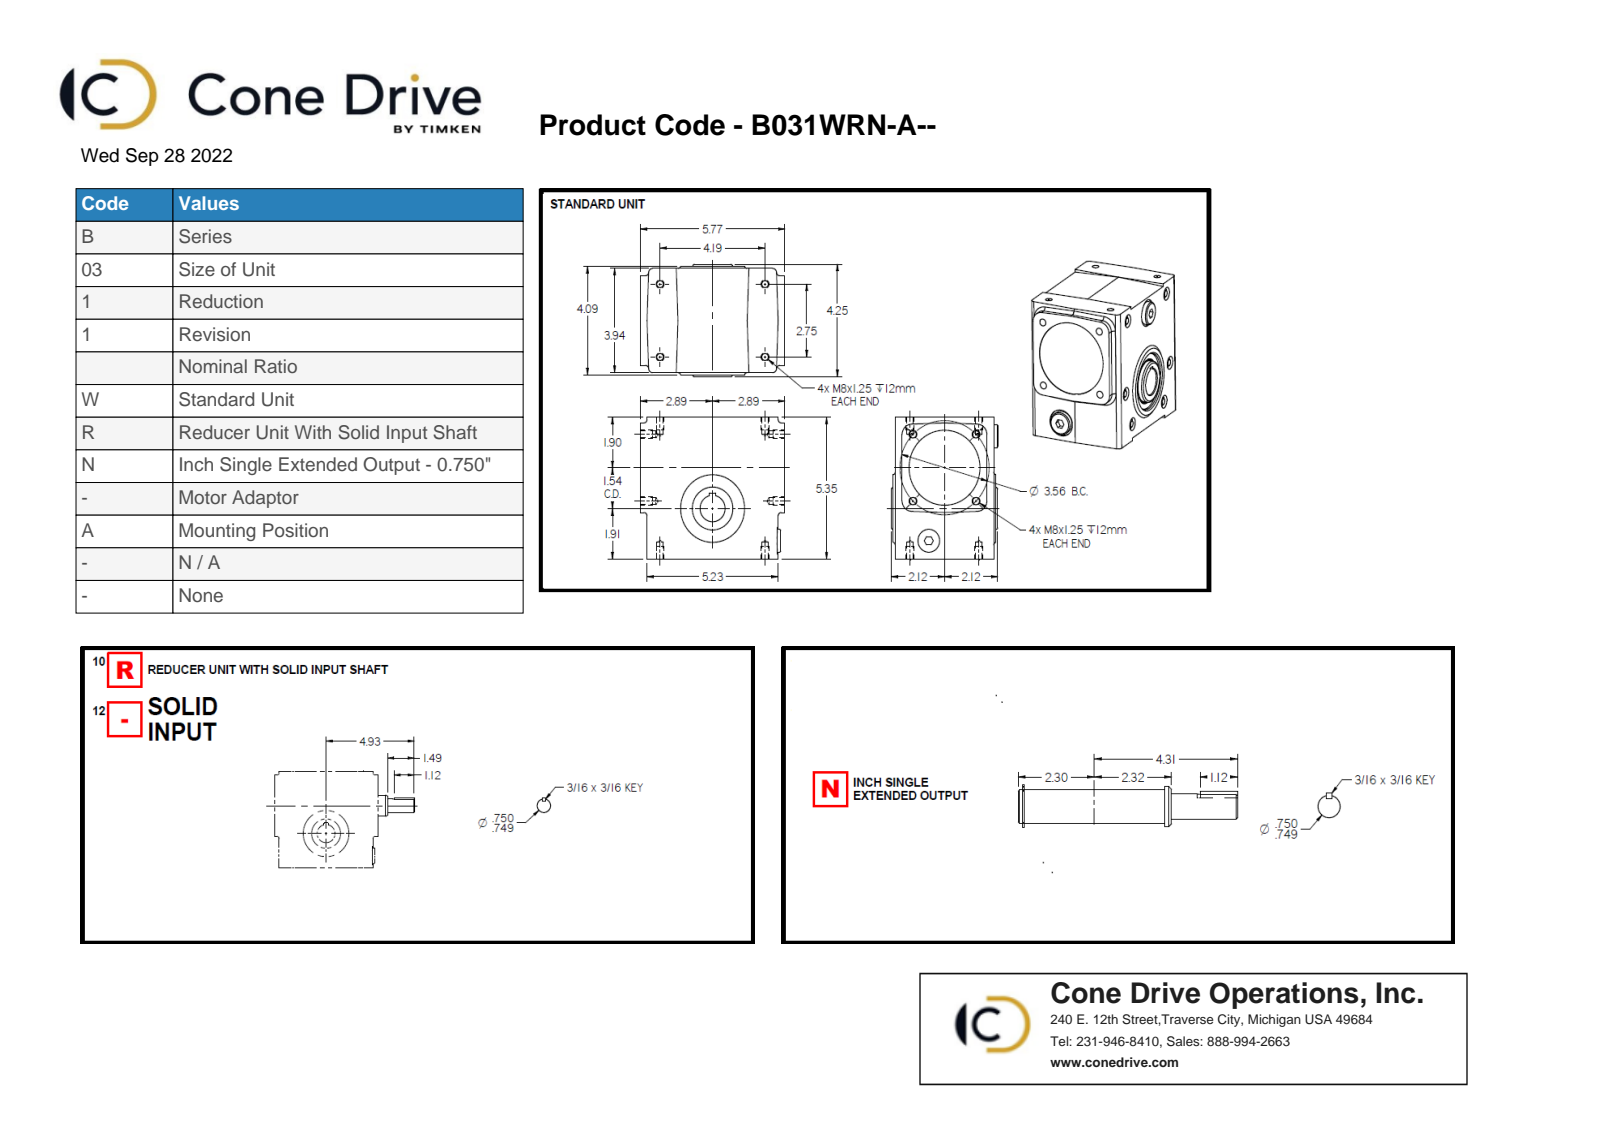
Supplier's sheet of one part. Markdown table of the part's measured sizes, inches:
| quantity | value |
| --- | --- |
| part name | B031110.WRN-A; B03-1-CP; B03-0610-X-CP; B03-0N-CP |
| STEP written by | Solid Edge (AUTOMOTIVE_DESIGN) |
| units | inches |
| bodies | 11 solids, 454 faces (237 planar, 124 cylindrical, 93 other) |
| overall size | 7.756 × 6.609 × 5.394 |
| volume | 98.19 in³ |
| surface area | 326.9 in² |
| round holes (diameter × count) | 0.492 × 6, 0.262 × 4, 0.272 × 4, 0.078 × 2, 1.024 × 2, 0.63 × 1, 0.748 × 1, 1 × 1, 1 × 1, 1.119 × 1, 1.575 × 1, 1.687 × 1 |
| round bosses / shafts (diameter × count) | 0.394 × 6, 0.236 × 6, 0.02 × 3, 0.866 × 2, 0.75 × 2, 2.804 × 1, 1.766 × 1, 1.732 × 1 |
| partial cylindrical surfaces (radius × count) | 0.125 × 12, 0.01 × 4, 0.157 × 4, 0.394 × 4, 0.024 × 2, 0.094 × 2, 0.1 × 2, 0.5 × 2 |
| main face-to-face distances | 3.935, 0.669, 5.102, 5.348, 0.571, 0.098, 5.673, 5.004, 5.772, 5.354 |
| hole center spacings | 1.781, 2.52, 0.571, 1.489, 1.746, 1.774, 1.789, 1.852 |
